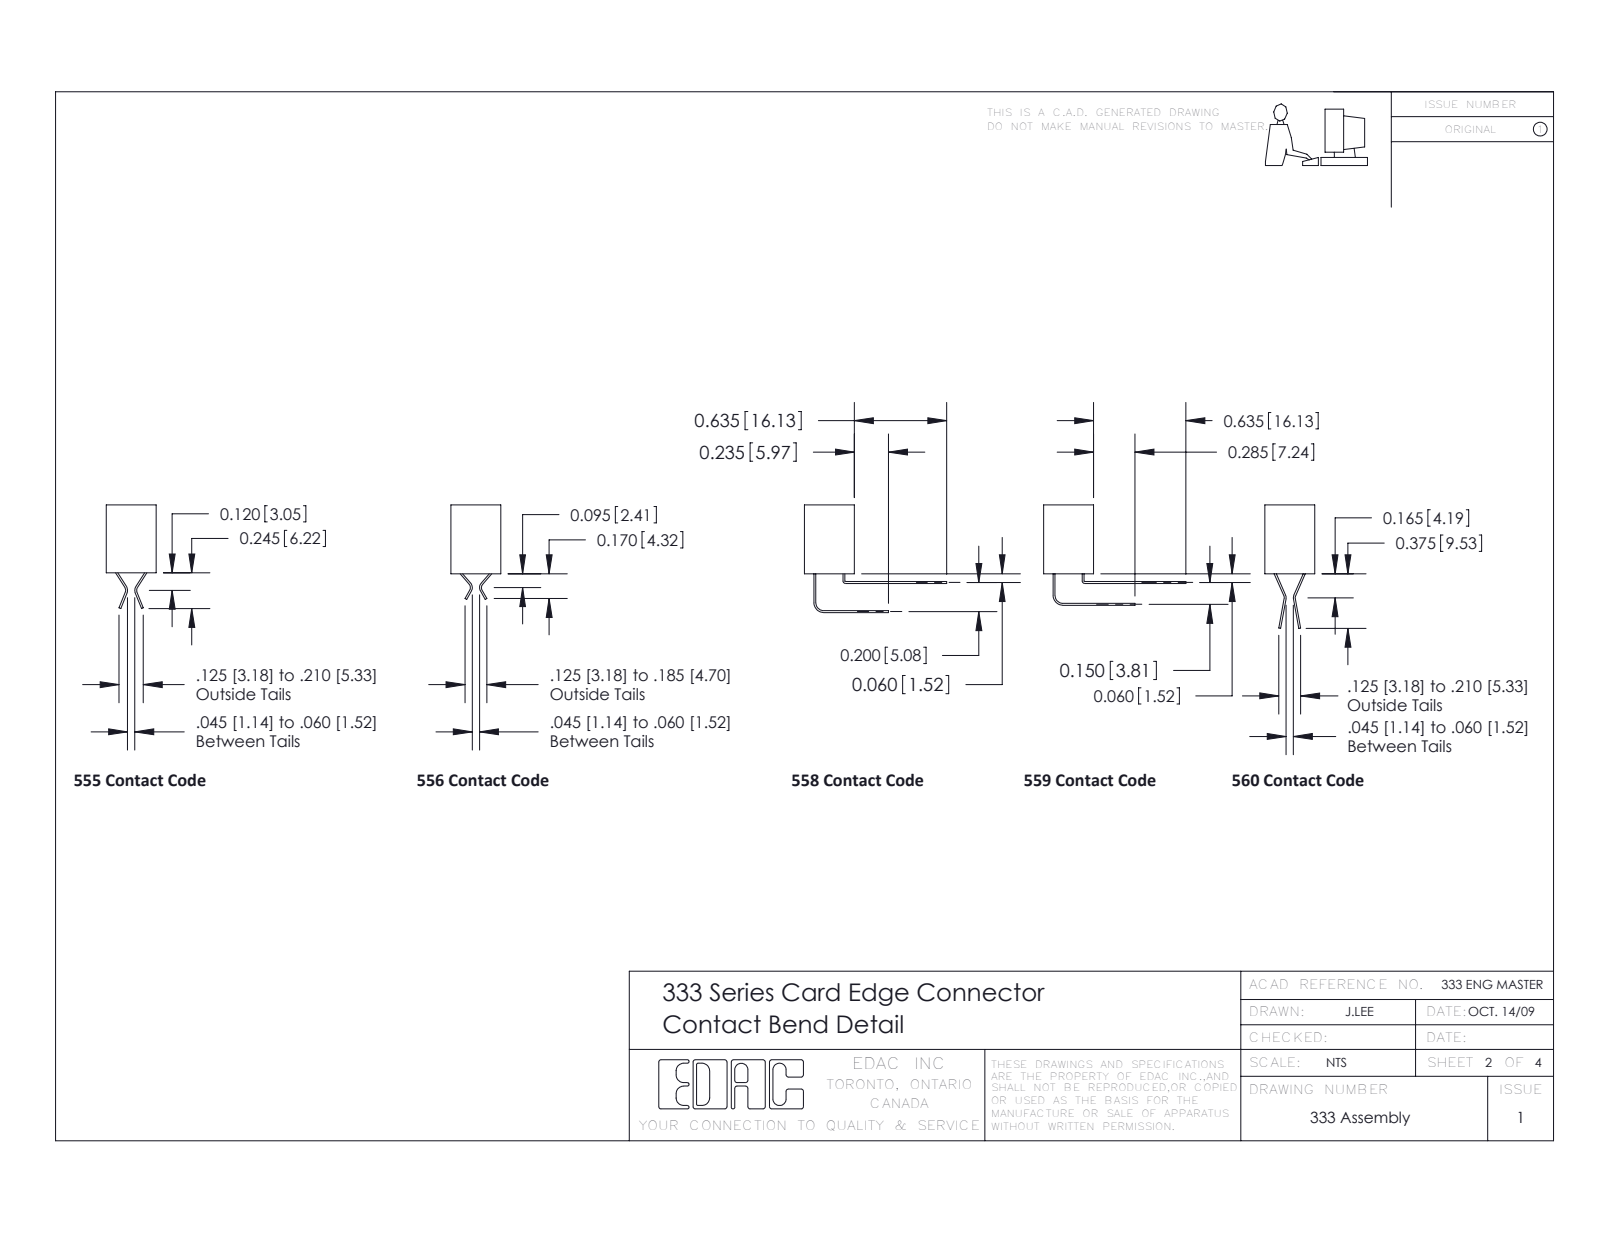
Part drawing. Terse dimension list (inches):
name: 333 Part_Offset - .156 Dia - TH; 333-012-500-803; 345-250-002_345-250-002-102; 345-292-001_345-293-100
written by: SolidWorks 2016 (CONFIG_CONTROL_DESIGN)
unit: in
bodies: 15 solids, 732 faces (444 planar, 280 cylindrical, 8 other)
size: 1.784 × 0.86 × 0.37
volume: 0.251 in³; area: 7.836 in²
holes: 2× ⌀0.116, 2× ⌀0.156
bosses: 2× ⌀0.25, 2× ⌀0.18, 2× ⌀0.136
rounds: 22× R0.01, 18× R0.006, 13× R0.02, 12× R0.016, 6× R0.007, 6× R0.031, 3× R0.026, 2× R0.014
face distances: 0.37, 0.156, 0.05, 0.072, 0.298, 0.076, 0.148, 0.222, 0.15, 0.206
hole spacings: 1.534
